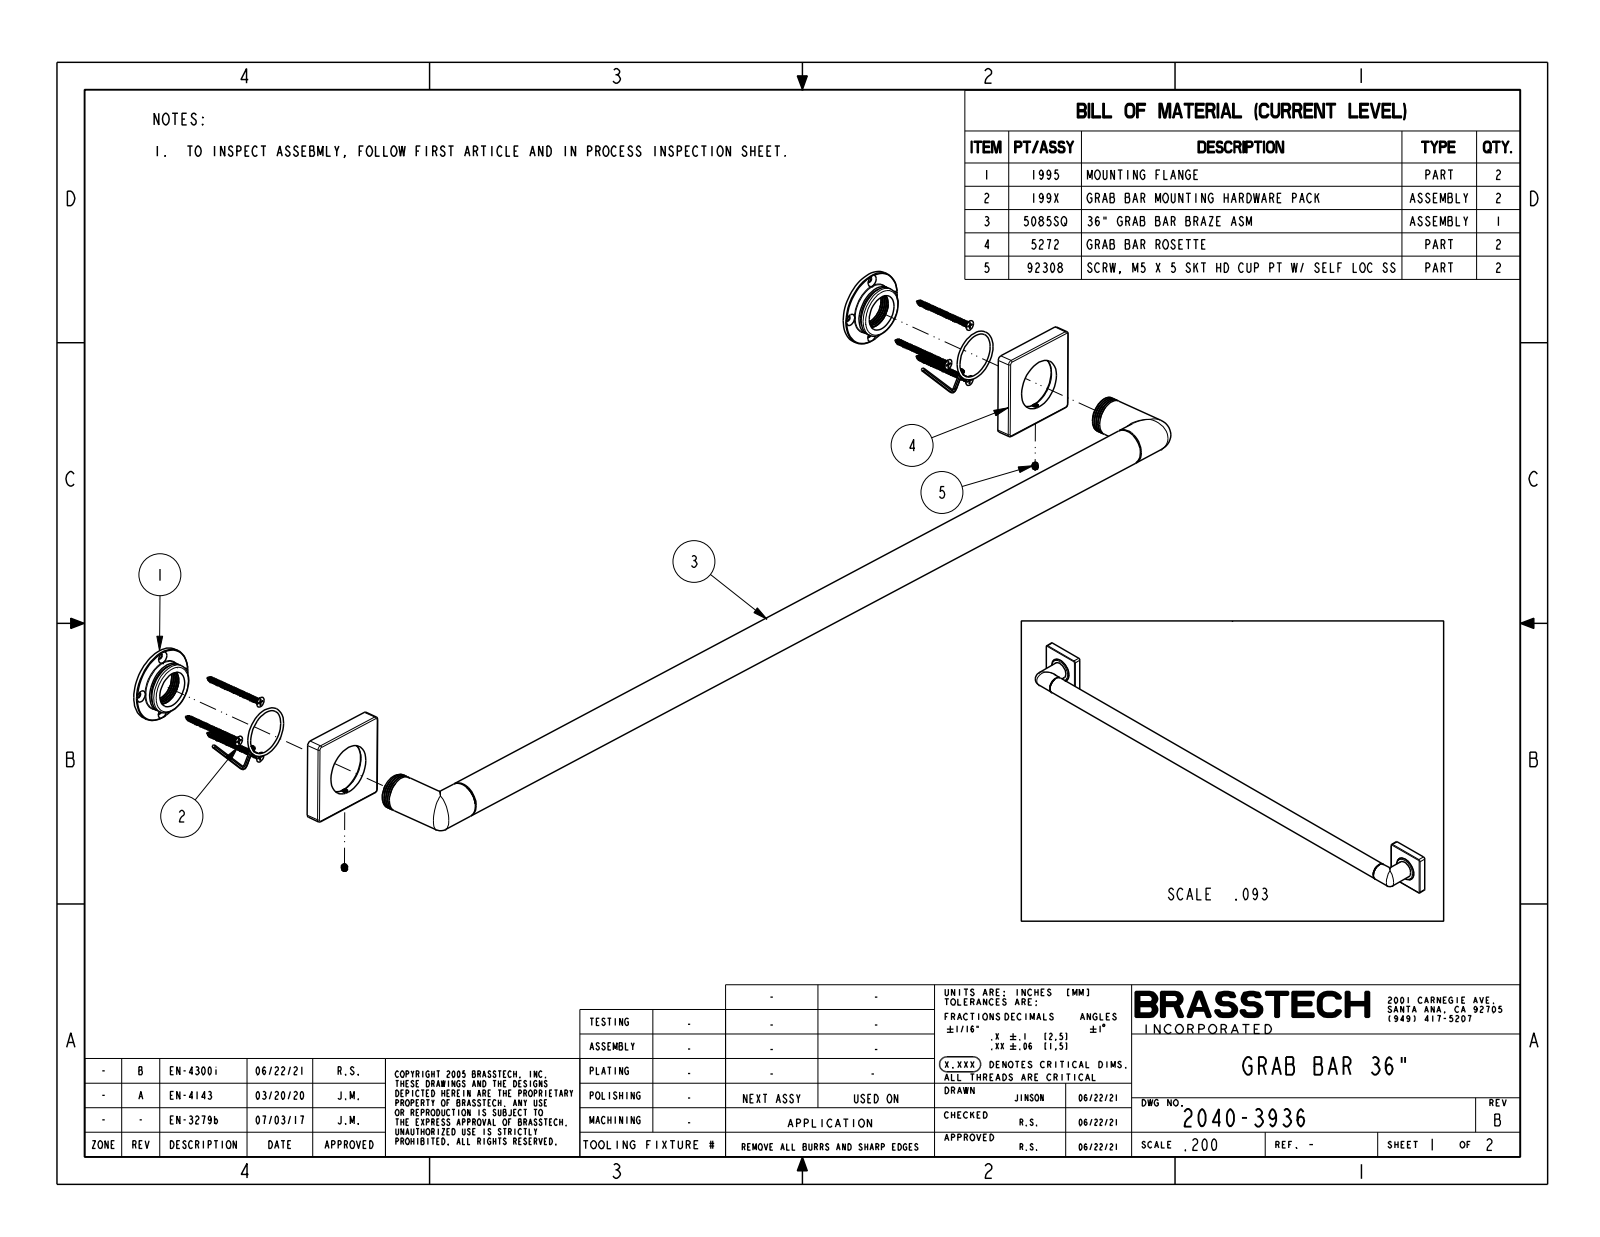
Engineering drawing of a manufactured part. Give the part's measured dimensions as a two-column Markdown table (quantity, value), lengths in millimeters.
| quantity | value |
| --- | --- |
| part name | 2040-3936 |
| STEP written by | CREO PARAMETRIC BY PTC INC, 2018400 (CONFIG_CONTROL_DESIGN) |
| units | millimeters |
| bodies | 1 solid, 72 faces (14 planar, 30 cylindrical, 28 other) |
| overall size | 990.6 × 76.2 × 70 |
| volume | 945 900 mm³ |
| surface area | 128 500 mm² |
| round bosses / shafts (diameter × count) | 31.8 × 3, 44.5 × 2 |
| partial cylindrical surfaces (radius × count) | 3.2 × 8, 1.3 × 6 |
| main face-to-face distances | 13.5, 76.2, 914.4, 15.2, 1.8, 990.6, 838.2 |
